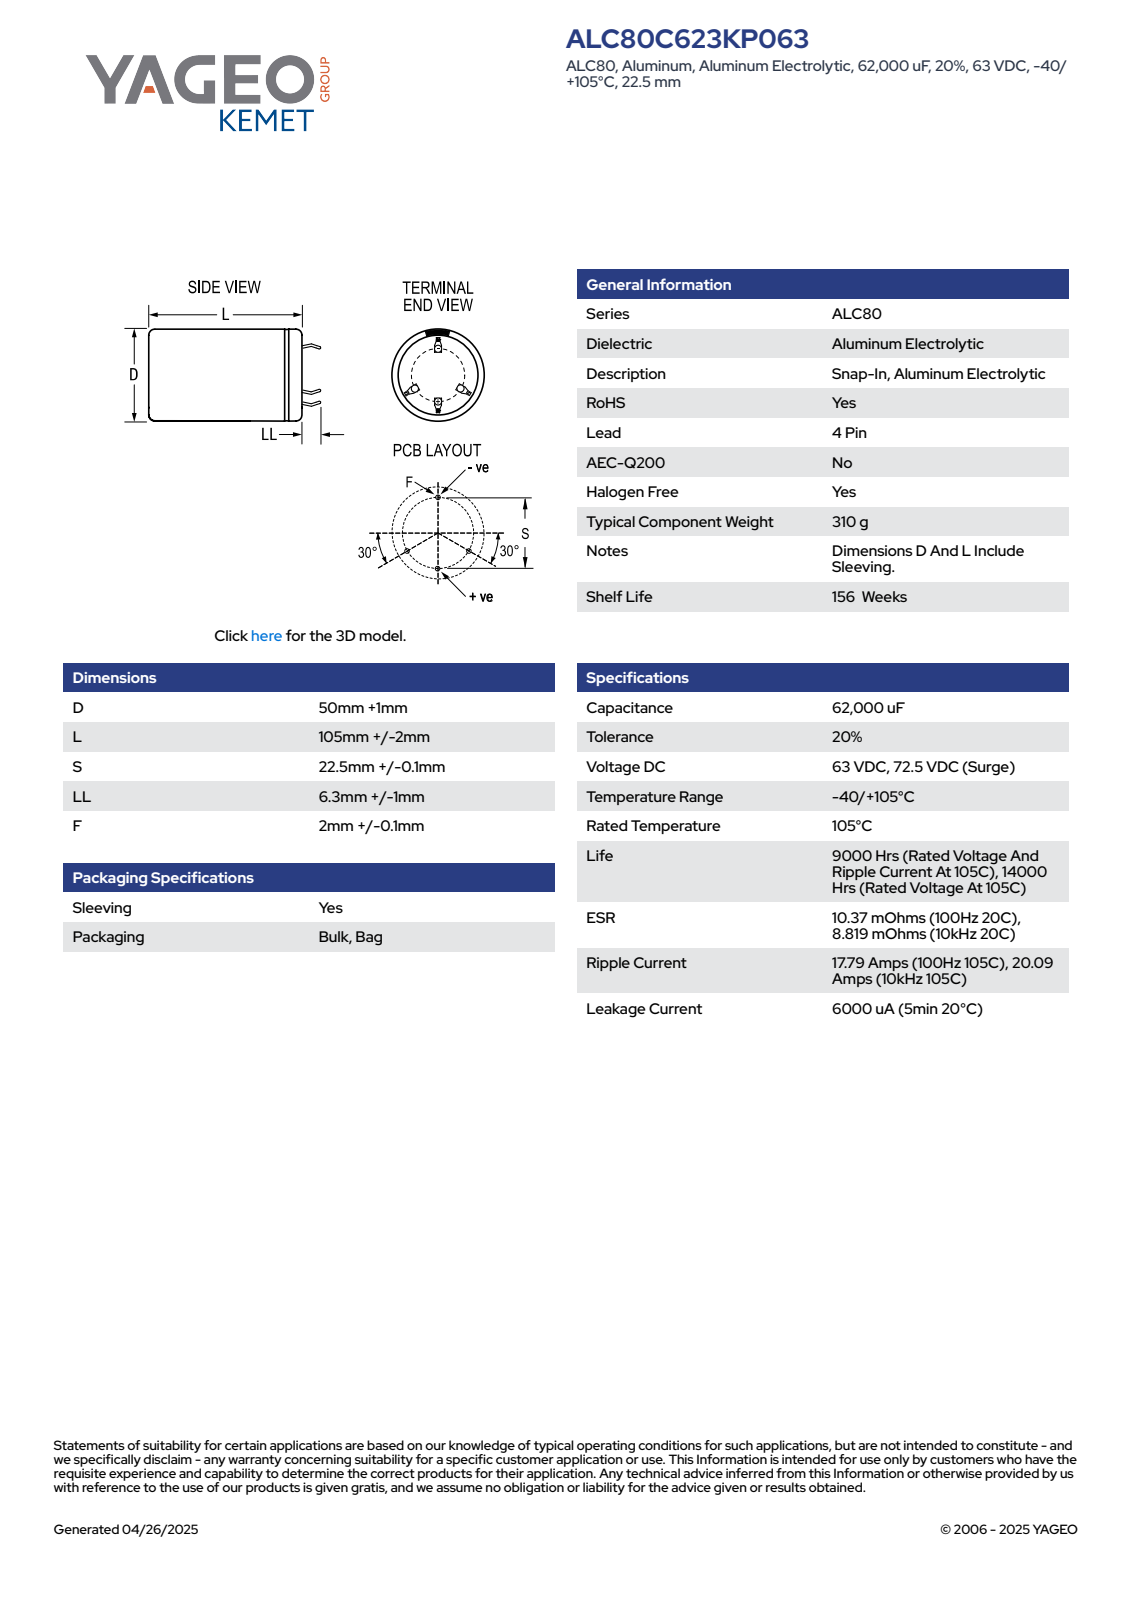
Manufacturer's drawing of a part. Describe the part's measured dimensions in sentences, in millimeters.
The part is named "CARS_K4P_50X105_D51L107S22.5LL7.3F2.1". Its 3-D file was written by "SolidWorks 2014 (AUTOMOTIVE_DESIGN)". It is 1 solid with 134 faces: 80 planar, 15 cylindrical and 39 other. Overall it measures 114.29 by 51 by 51 millimeters. Its volume is 217 077 cubic millimeters and its surface area 21 256 square millimeters. Round holes: 1 of diameter 45.12. Round bosses or shafts: 1 of diameter 51. Partial cylindrical surfaces (rounded edges, fillets, slot ends): 1 of radius 25.49. The main face-to-face distances are 106.99, 107.49, 0.5, 0.6, 16.94, 0.75, 1.35, 17.23, 16.65, 2.1.
